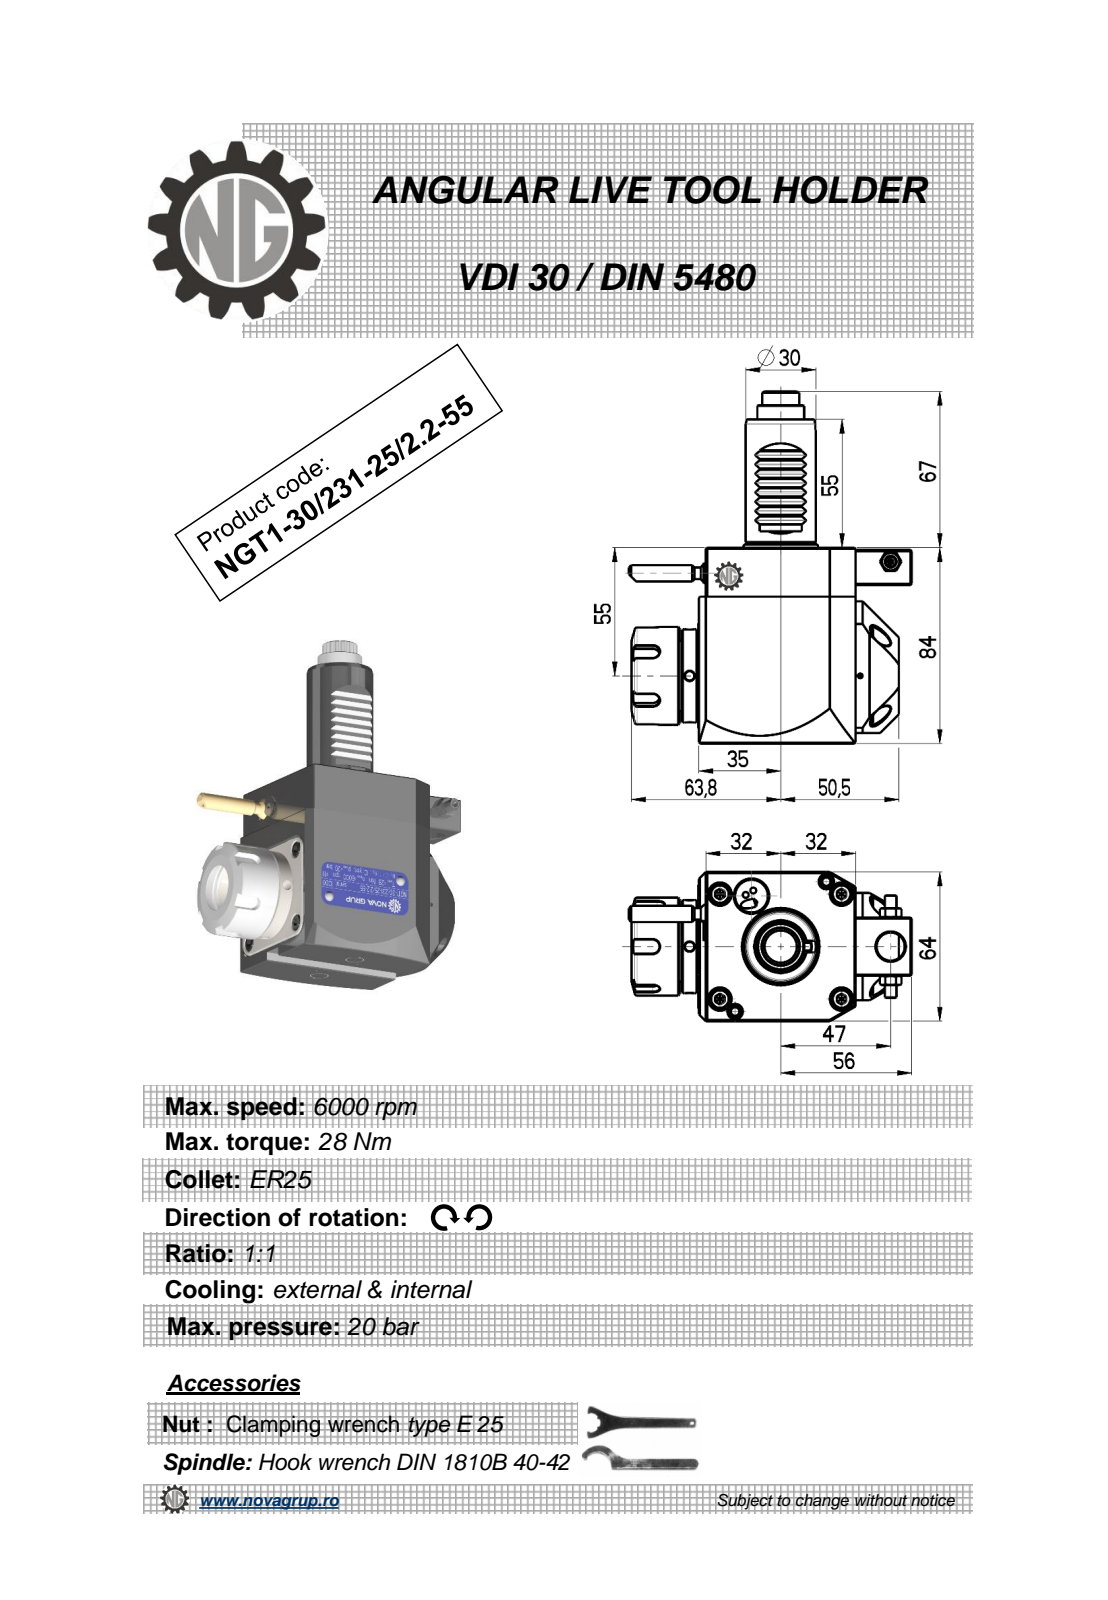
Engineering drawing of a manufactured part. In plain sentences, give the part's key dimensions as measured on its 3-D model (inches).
The part is named "NGT1_30_231_25_2_2_55". Its 3-D file was written by "PRO/ENGINEER BY PARAMETRIC TECHNOLOGY CORPORATION, 2010280 (CONFIG_CONTROL_DESIGN)". It is 1 solid with 498 faces: 184 planar, 157 cylindrical and 157 other. Overall it measures 5.945 by 4.759 by 2.583 inches. Its volume is 28.21 cubic inches and its surface area 73.91 square inches. Round holes: 2 of diameter 0.157, 1 of diameter 0.098, 1 of diameter 0.118, 1 of diameter 0.165, 1 of diameter 0.374, 1 of diameter 0.472, 1 of diameter 0.799. Round bosses or shafts: 2 of diameter 0.353, 2 of diameter 0.197, 1 of diameter 1.654, 1 of diameter 1.575, 1 of diameter 1.299, 1 of diameter 1.181, 1 of diameter 0.787, 1 of diameter 0.276. Partial cylindrical surfaces (rounded edges, fillets, slot ends): 36 of radius 0.078, 12 of radius 0.01, 8 of radius 0.012, 5 of radius 0.118, 2 of radius 6.299, 1 of radius 0.279, 1 of radius 0.312, 1 of radius 0.512. The main face-to-face distances are 2.52, 3.307, 2.646, 2.638, 0.126, 0.118, 0.728, 0.02, 3.374, 3.366. The hole center spacings are 0.56, 1.818, 1.831, 3.384, 3.895.
